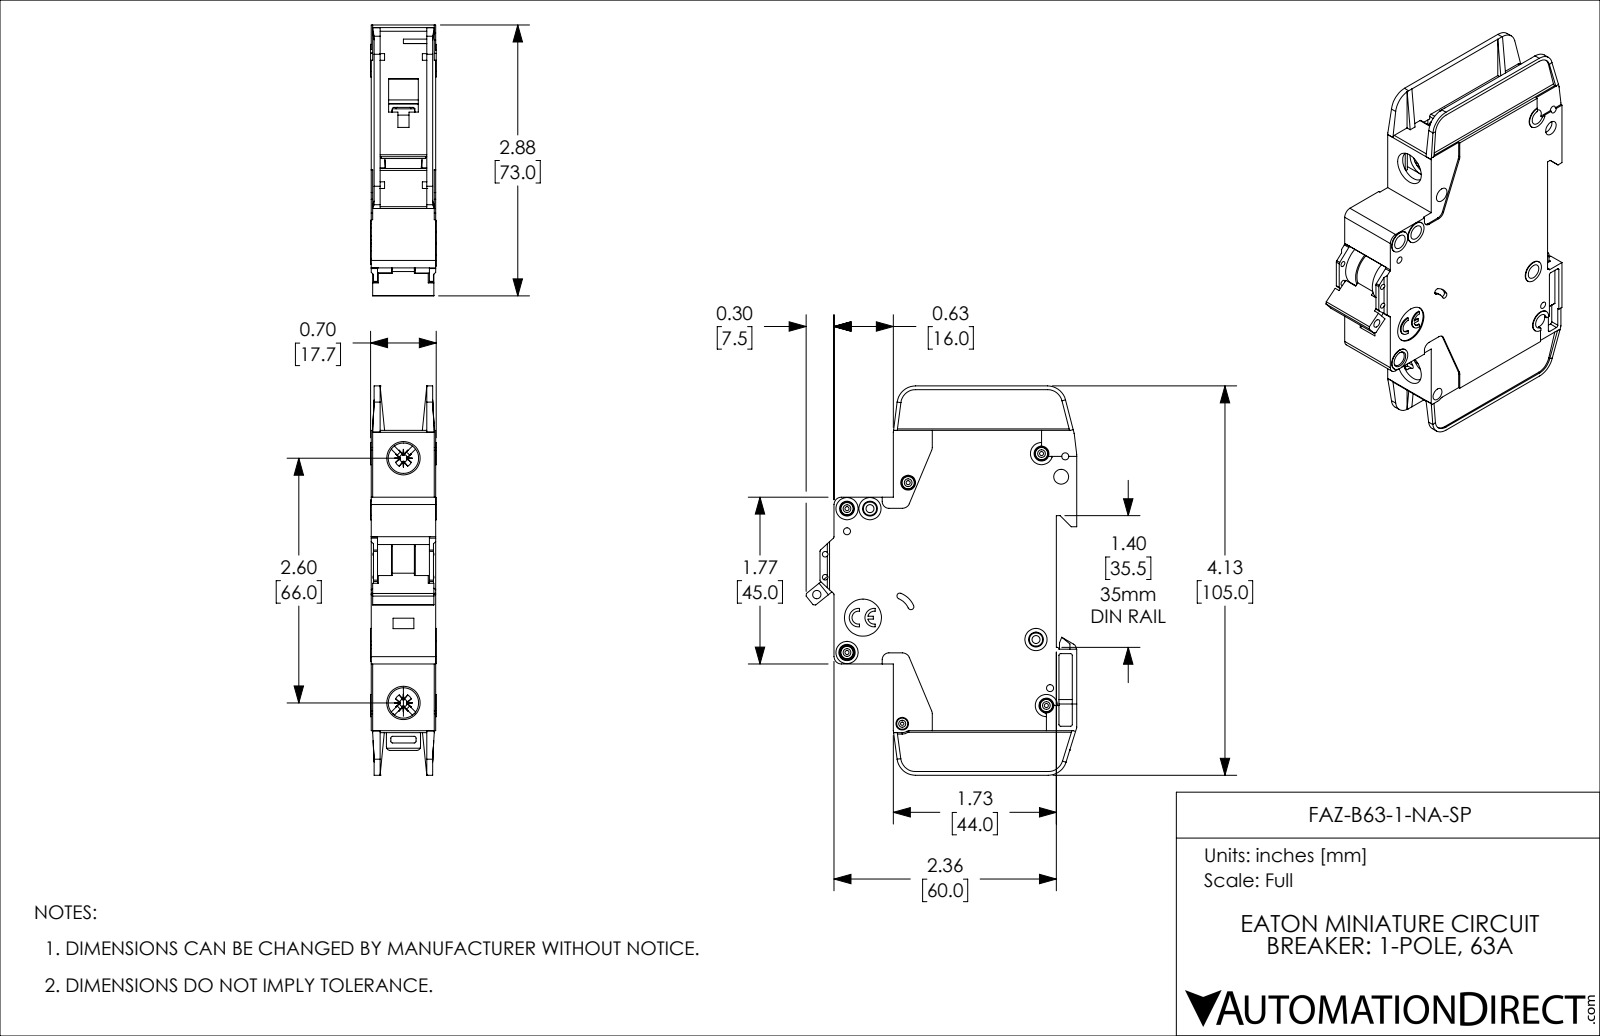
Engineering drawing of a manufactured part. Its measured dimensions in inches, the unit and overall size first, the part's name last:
Units: inches
Overall size (bounding box): 4.134 × 2.876 × 0.697
Round holes (diameter × count): ⌀0.157 ×8, ⌀0.043 ×5, ⌀0.075 ×4, ⌀0.059 ×2, ⌀0.085 ×2, ⌀0.323 ×2, ⌀0.035 ×1, ⌀0.089 ×1, ⌀0.098 ×1, ⌀0.134 ×1, ⌀0.394 ×1
Round bosses / shafts (diameter × count): ⌀0.13 ×5, ⌀0.236 ×4, ⌀0.118 ×2, ⌀0.098 ×1
Partial cylindrical surfaces — rounded edges, fillets, slot ends (radius × count): R0.02 ×42, R0.016 ×10, R0.039 ×10, R0.079 ×8, R0.197 ×5, R0.008 ×4, R0.026 ×4, R0.043 ×4
Main face-to-face distances: 0.047, 0.685, 0.591, 0.638, 0.094, 0.543, 0.016, 0.031, 0.496, 0.575
Hole centre spacings: 0.244, 0.537, 0.87, 0.189, 0.199, 0.204, 0.221, 0.24
Volume: 4.682 in³ · Surface area: 41.01 in²
Bodies: 1 solid, 1127 faces (671 planar, 357 cylindrical, 99 other)
Part name (STEP PRODUCT): FAZ-B63-1-NA-SP
STEP written by: SolidWorks 2019 (AUTOMOTIVE_DESIGN)
